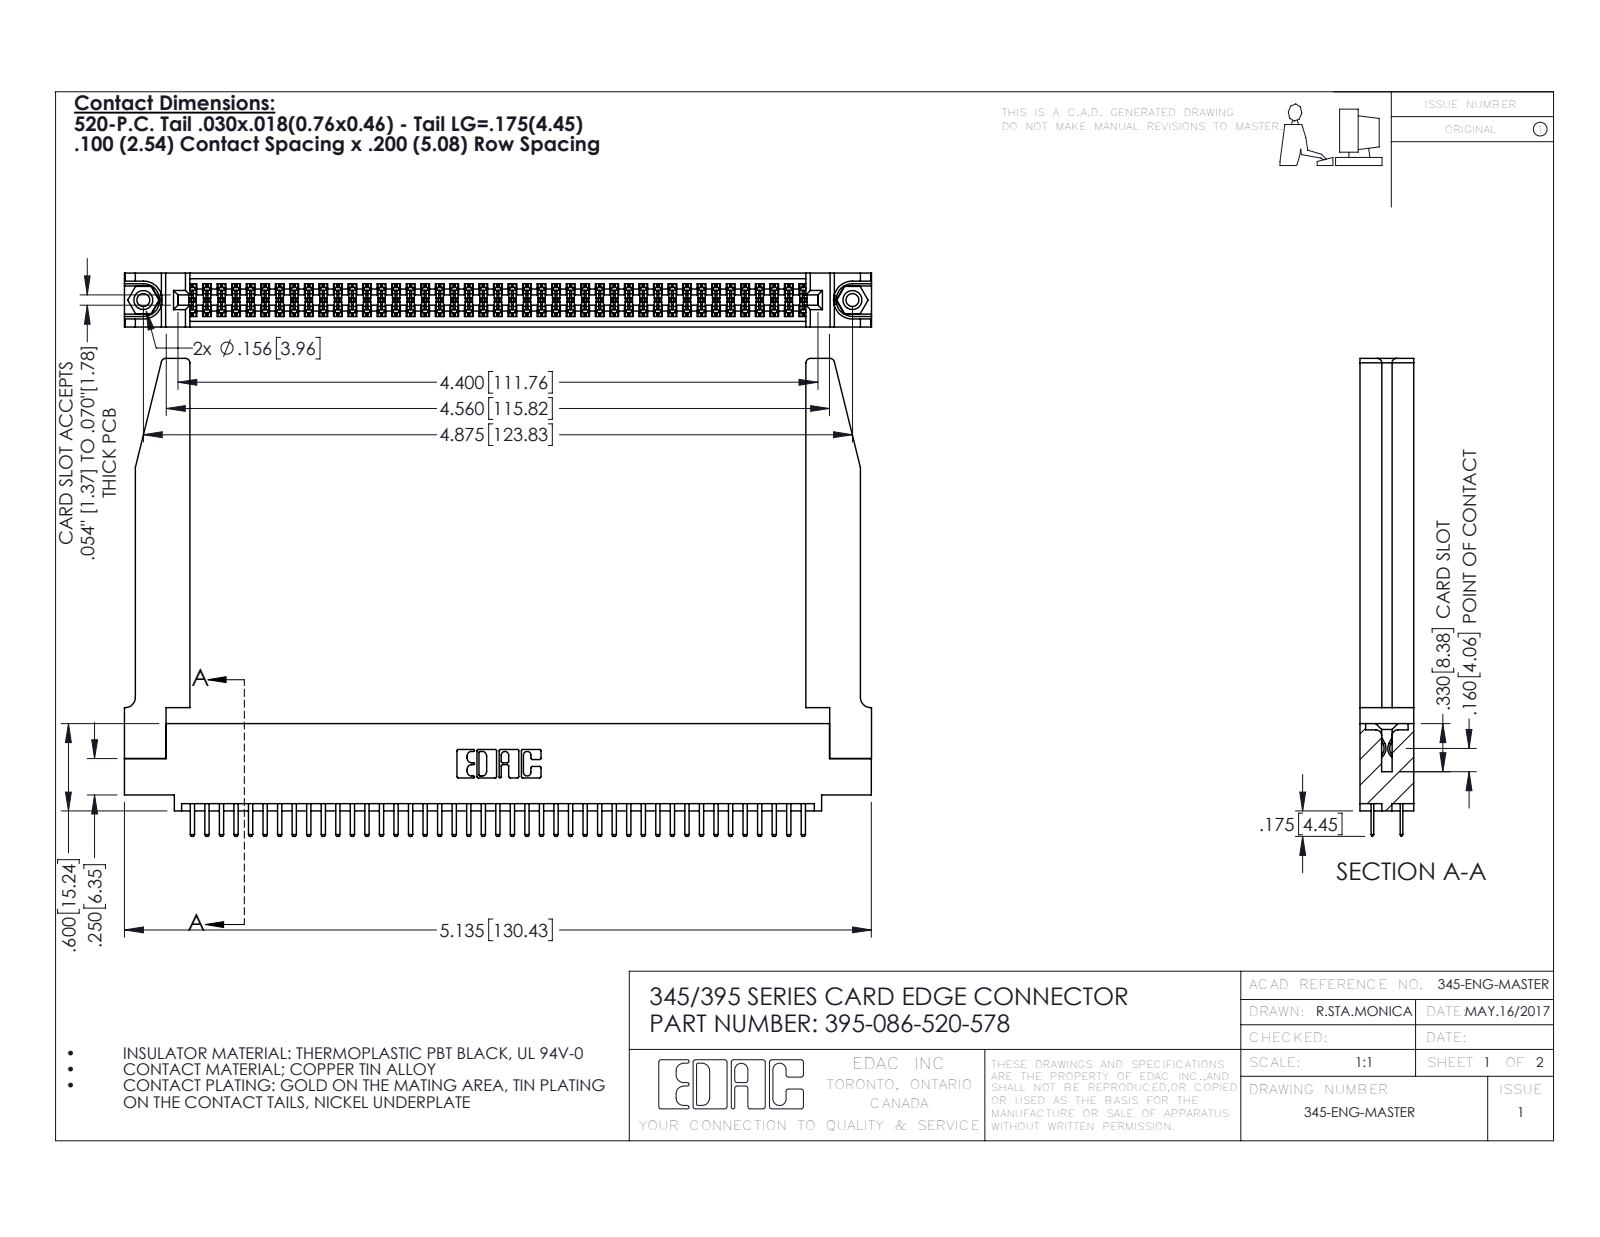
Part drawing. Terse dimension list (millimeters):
name: 345 Part_0.110 Offset - 0.156 Dia-TH; 345-250-001_345-250-001-102; 345-292-001_345-293-120; 345-220-078_345-220-078 (+1 more)
written by: SolidWorks 2016 (CONFIG_CONTROL_DESIGN)
unit: mm
bodies: 91 solids, 5008 faces (3236 planar, 1720 cylindrical, 52 other)
size: 130.5 × 83.4 × 9.4
volume: 20 340 mm³; area: 25 450 mm²
holes: 2× ⌀2.3, 2× ⌀3.2, 2× ⌀4, 1× ⌀1.6
bosses: 2× ⌀3.9
rounds: 129× R0.2, 90× R0.3, 22× R0.3, 8× R0.8, 6× R0.2, 6× R0.8, 3× R0.7, 2× R0.4
face distances: 9.4, 1.8, 7.6, 5.1, 2.5, 6.9, 0.6, 5.7, 0.6, 4.4
hole spacings: 6.9, 117.8, 123.8
